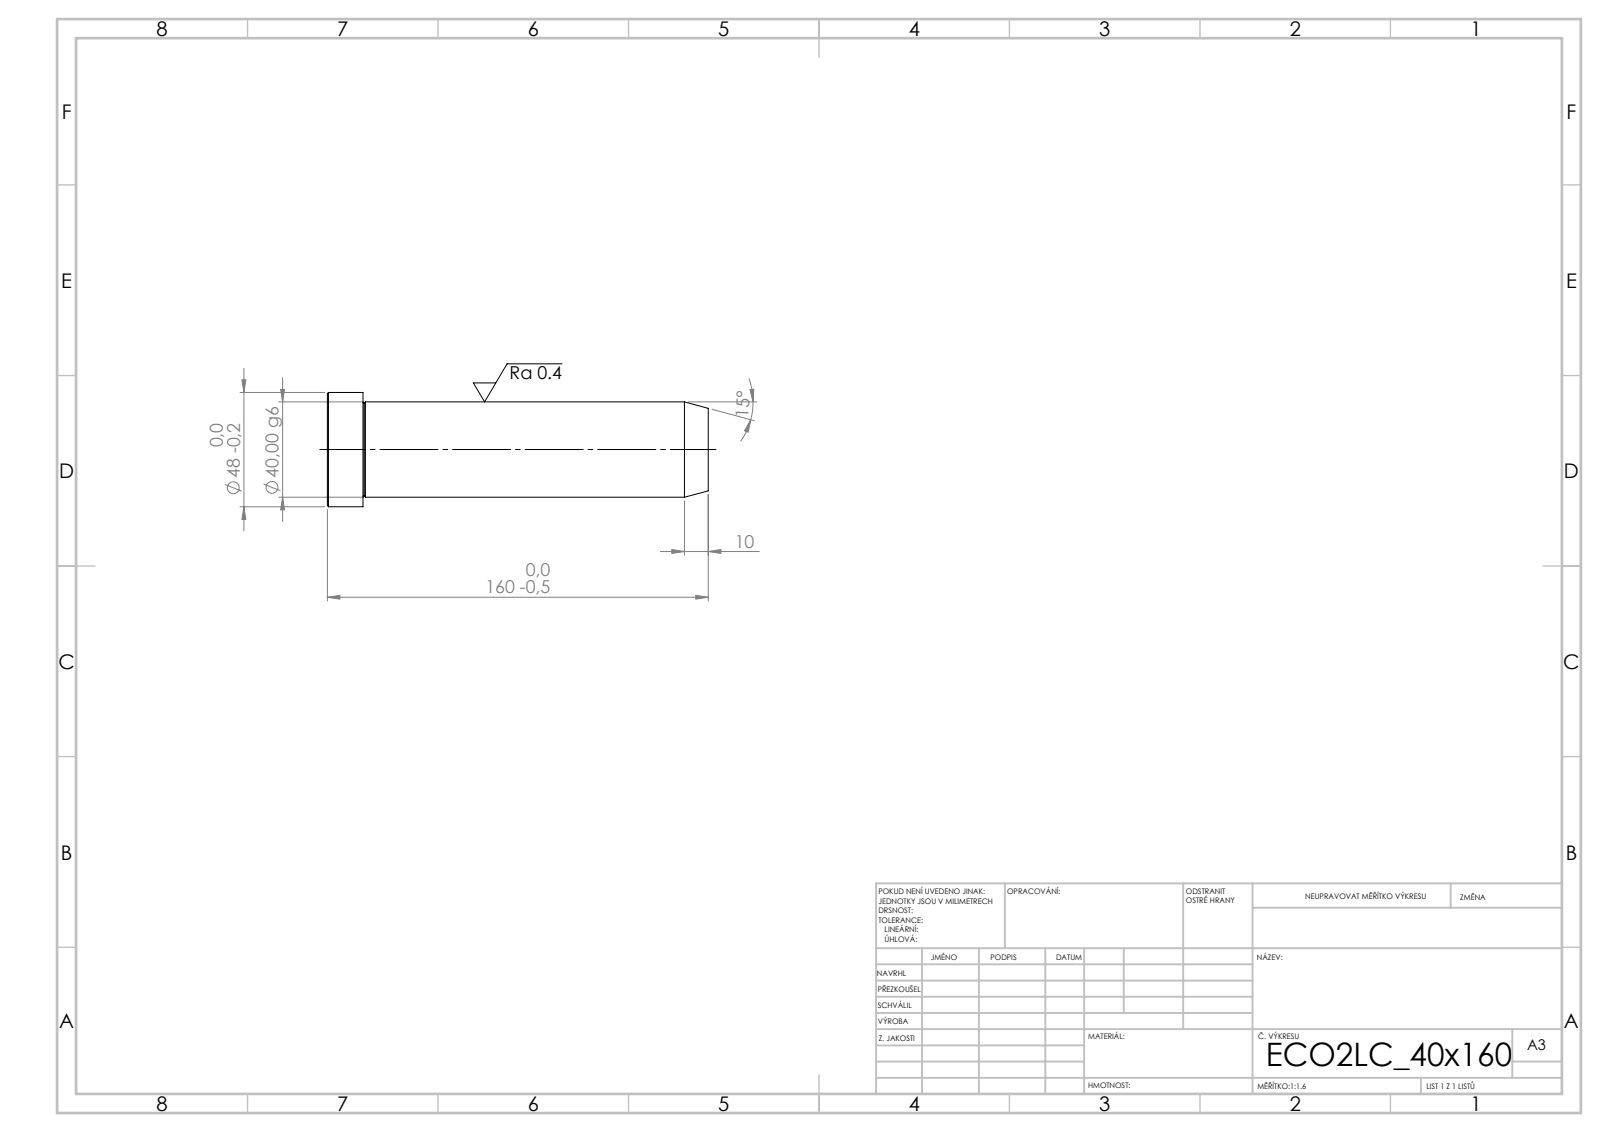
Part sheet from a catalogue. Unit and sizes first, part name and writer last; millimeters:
Units: millimetres
Overall size (bounding box): 160 × 48 × 48
Round bosses / shafts (diameter × count): ⌀48 ×1, ⌀40 ×1
Main face-to-face distances: 160, 145, 15
Volume: 207 680 mm³ · Surface area: 23 769 mm²
Bodies: 1 solid, 15 faces (3 planar, 4 cylindrical, 8 other)
STEP written by: SolidWorks 2019 (CONFIG_CONTROL_DESIGN)
